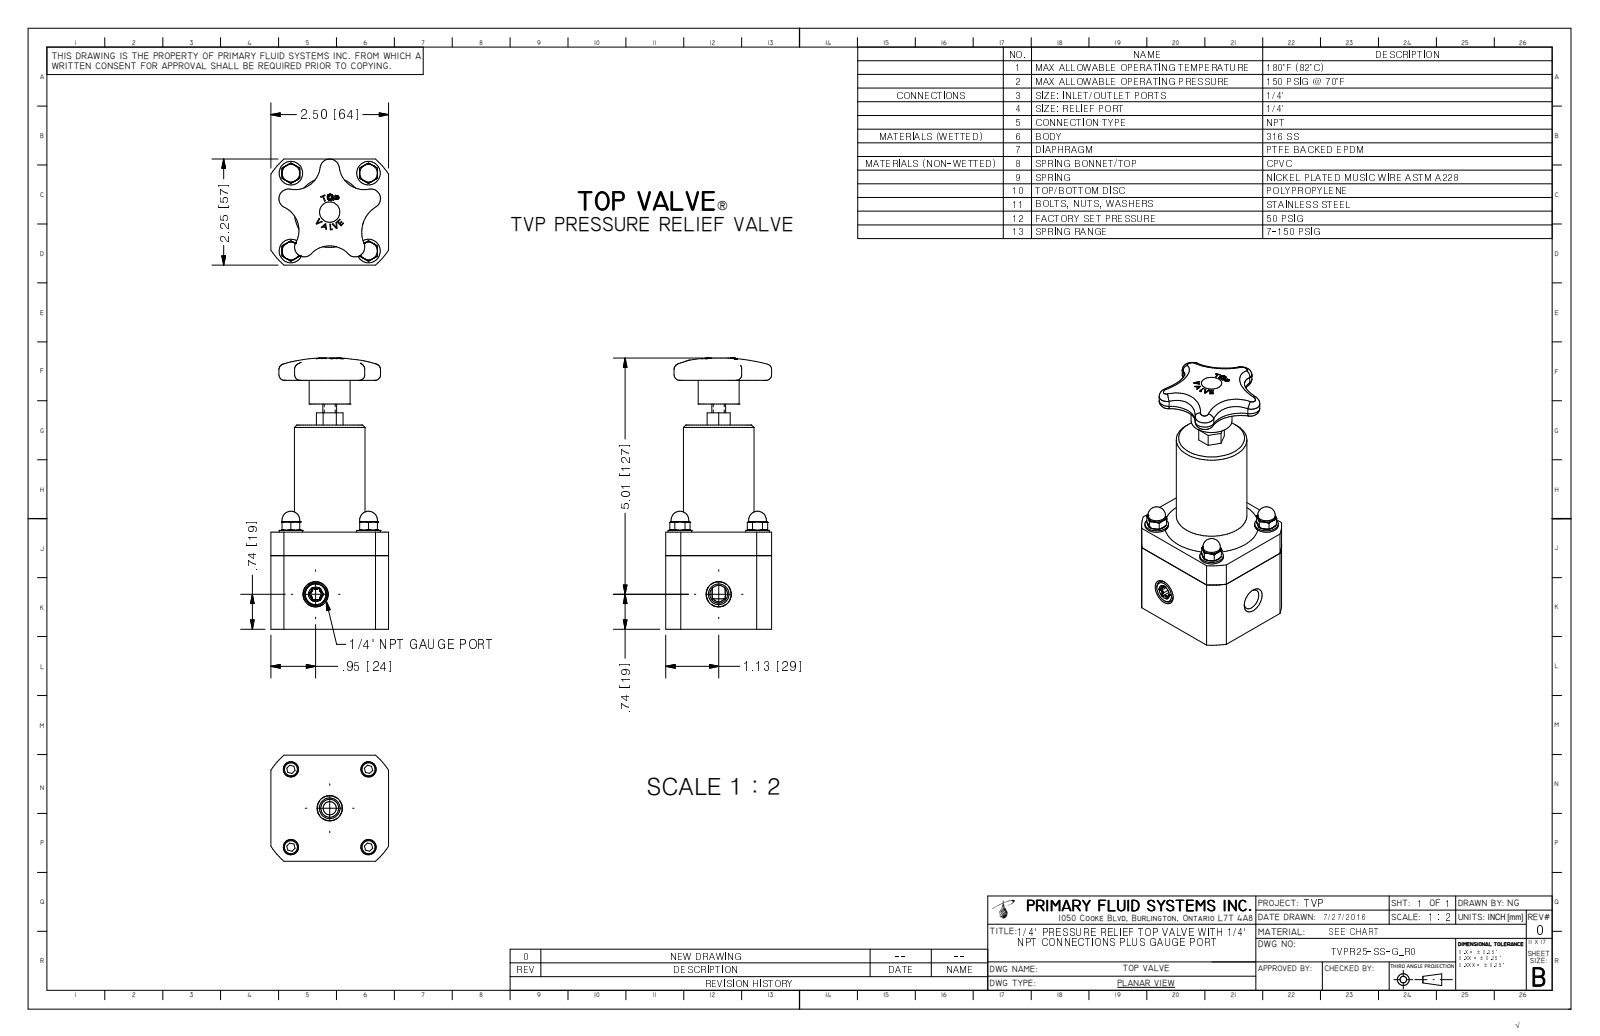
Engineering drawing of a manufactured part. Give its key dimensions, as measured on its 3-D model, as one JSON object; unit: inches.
{"part_name": "TVPR25-SS-G_R0", "step_written_by": "Autodesk Inventor 2009 (AUTOMOTIVE_DESIGN)", "units": "inches", "bodies": {"solids": 1, "faces": 378, "planar": 155, "cylindrical": 54, "other": 169}, "overall_size": [5.75, 2.5, 2.25], "volume_in3": 16.39, "surface_area_in2": 56.68, "round_holes": [[0.147, 4], [0.437, 2], [1.525, 1]], "round_bosses_or_shafts": [[0.5, 4], [0.375, 4], [0.312, 4], [1.5, 1], [0.87, 1], [0.293, 1]], "partial_cylinders_radius": [[0.027, 6], [0.085, 5], [0.205, 5], [0.536, 4], [0.656, 4], [0.625, 1], [0.745, 1], [1.488, 1]], "face_to_face_distances": [2.25, 2.5, 2.06, 4.33, 2.27, 4.776, 2.716, 0.446, 2.096, 0.036], "hole_center_spacings": [1.167, 1.167, 1.65, 1.65, 2.334]}
